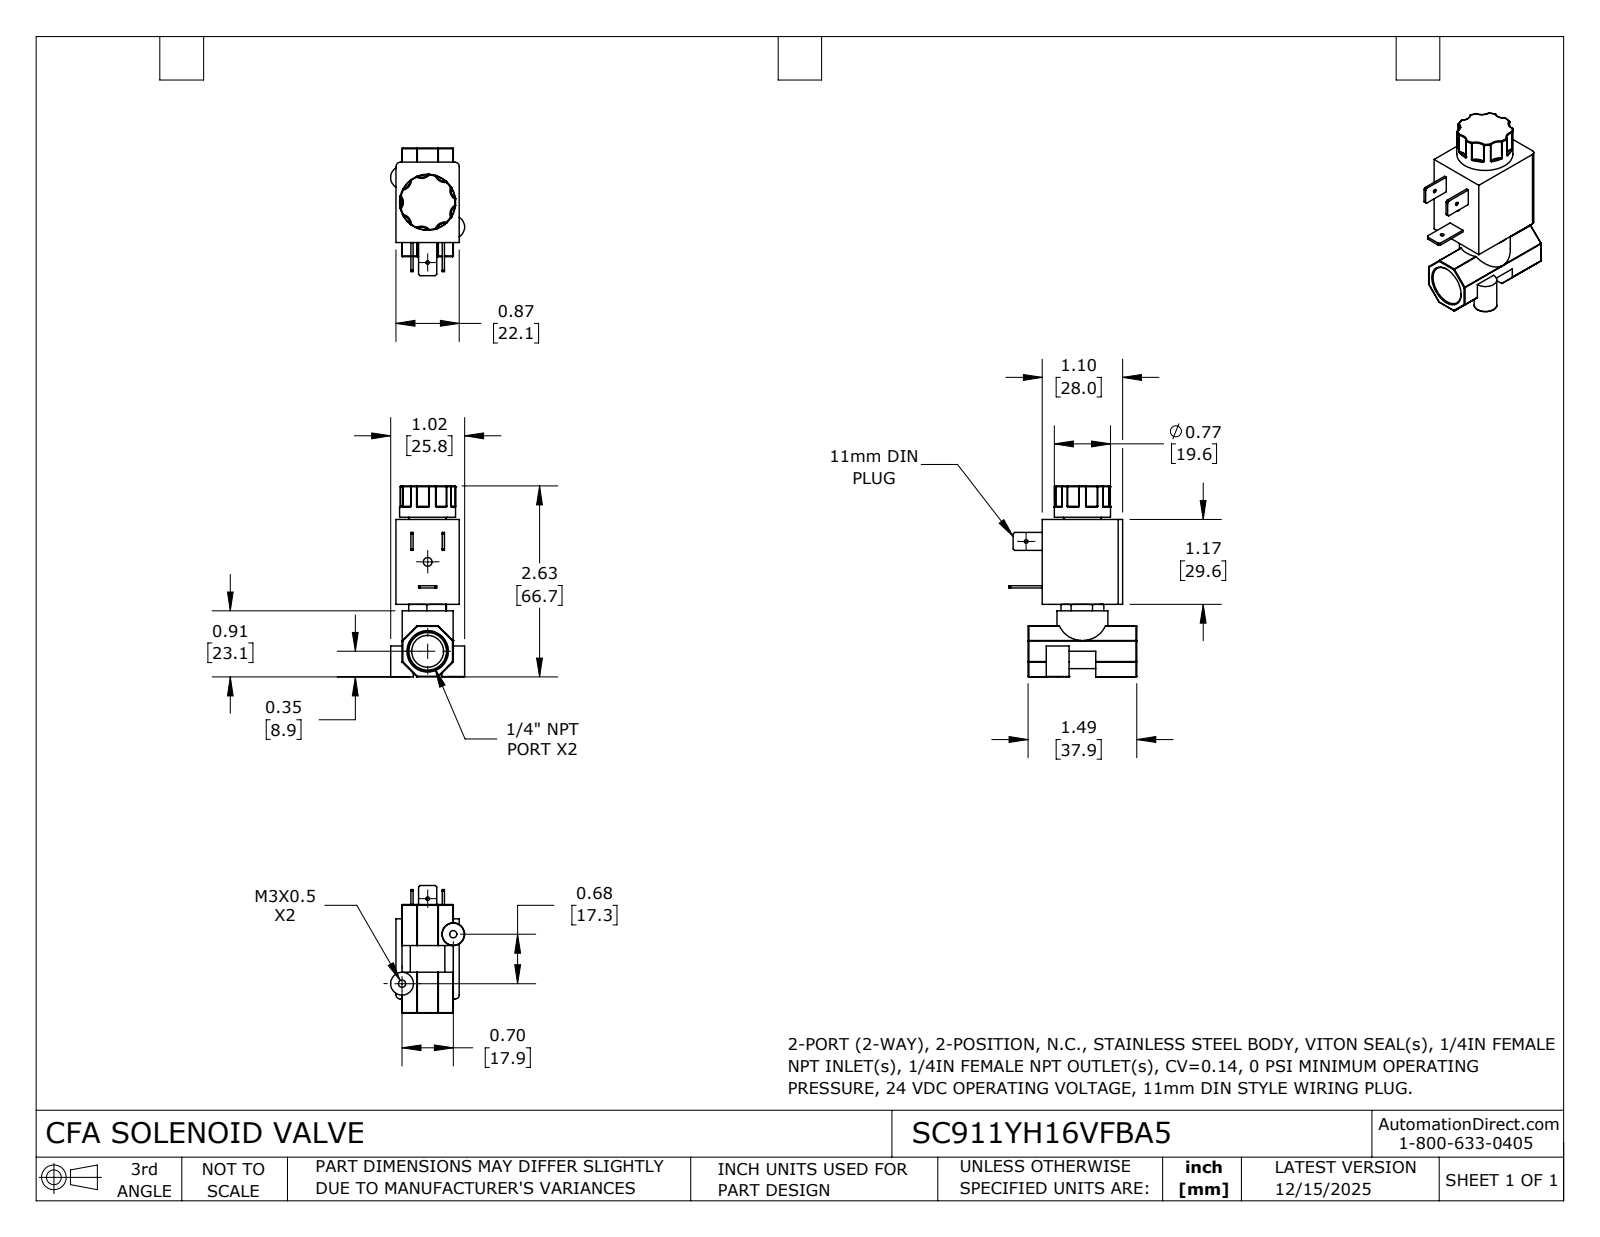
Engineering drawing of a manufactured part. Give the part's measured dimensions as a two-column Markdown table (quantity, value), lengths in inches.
| quantity | value |
| --- | --- |
| part name | SC911YH16VFBA5 |
| STEP written by | SolidWorks 2024 (CONFIG_CONTROL_DESIGN) |
| units | inches |
| bodies | 1 solid, 312 faces (74 planar, 89 cylindrical, 149 other) |
| overall size | 2.625 × 1.757 × 1.017 |
| volume | 1.799 in³ |
| surface area | 16.13 in² |
| round holes (diameter × count) | 0.05 × 2, 0.1 × 2, 0.12 × 1, 0.438 × 1 |
| round bosses / shafts (diameter × count) | 0.313 × 2, 0.77 × 1, 0.7 × 1 |
| partial cylindrical surfaces (radius × count) | 0.01 × 42, 0.133 × 7, 0.06 × 2, 0.132 × 2, 0.237 × 1 |
| main face-to-face distances | 0.87, 0.704, 1.104, 1.167, 0.083, 0.787, 0.46, 0.998, 2.165, 2.625 |
| hole center spacings | 0.602, 0.979, 1.22, 1.23 |
